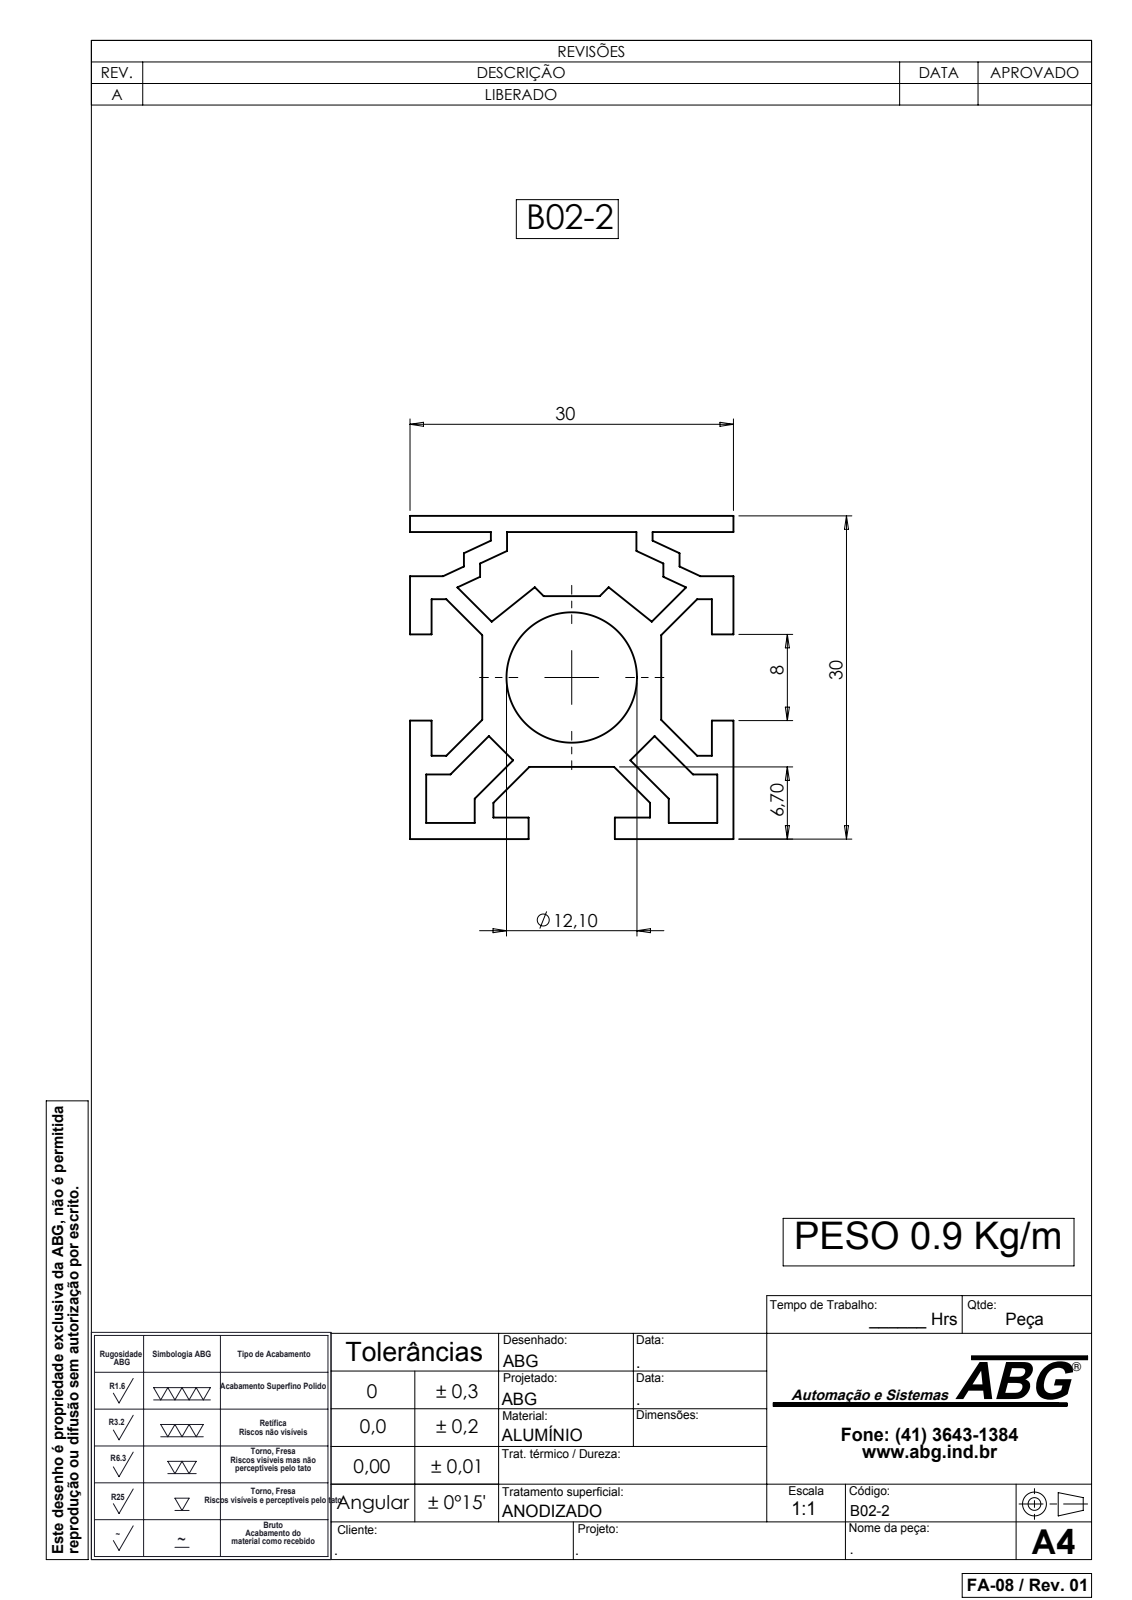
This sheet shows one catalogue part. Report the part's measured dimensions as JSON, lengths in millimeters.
{"part_name": "B02-2", "step_written_by": "SolidWorks 2007 (CONFIG_CONTROL_DESIGN)", "units": "millimeters", "bodies": {"solids": 1, "faces": 82, "planar": 80, "cylindrical": 2, "other": 0}, "overall_size": [6000, 30, 30], "volume_mm3": 2078000, "surface_area_mm2": 2166000, "round_holes": [[12.1, 1]], "face_to_face_distances": [1.5, 28.5, 30, 6.7, 23.3, 2, 28, 4.7, 4.68, 0.5]}
